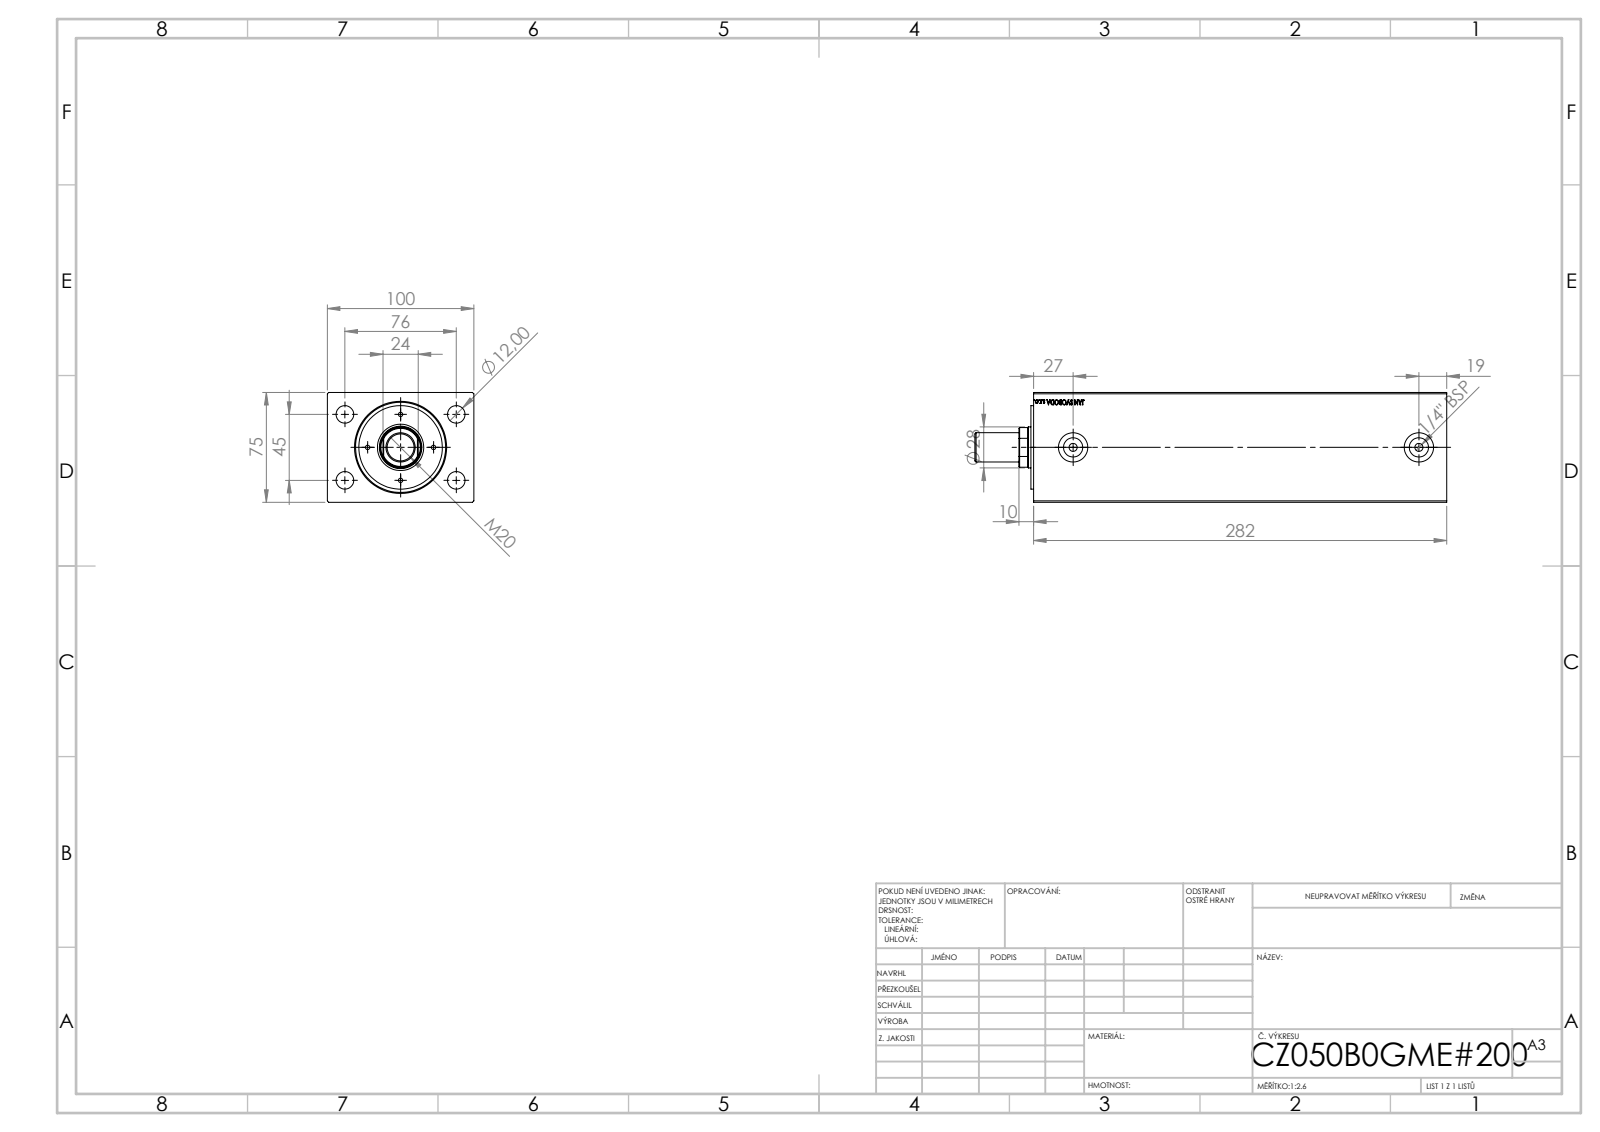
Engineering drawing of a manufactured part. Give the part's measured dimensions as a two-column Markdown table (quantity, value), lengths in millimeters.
| quantity | value |
| --- | --- |
| part name | V500CZ_B_VC; V500CZ_SMALL_MALE_METRIC; V500CZ |
| STEP written by | SolidWorks 2019 (CONFIG_CONTROL_DESIGN) |
| units | millimeters |
| bodies | 4 solids, 879 faces (401 planar, 60 cylindrical, 418 other) |
| overall size | 322 × 100 × 75 |
| volume | 1 897 000 mm³ |
| surface area | 229 138 mm² |
| round holes (diameter × count) | 3 × 4, 12 × 4, 5.5 × 2, 13.16 × 2, 20 × 2, 18.5 × 1, 28 × 1, 29 × 1, 36 × 1, 50 × 1, 61.5 × 1 |
| round bosses / shafts (diameter × count) | 57 × 1, 20 × 1 |
| partial cylindrical surfaces (radius × count) | 13.5 × 1 |
| main face-to-face distances | 75, 100, 282, 264.5, 17.5, 82, 182.5, 200, 1.8, 83.8 |
| hole center spacings | 22.5, 27.32, 31.82, 38, 44.16, 45, 58.9, 64.55 |
